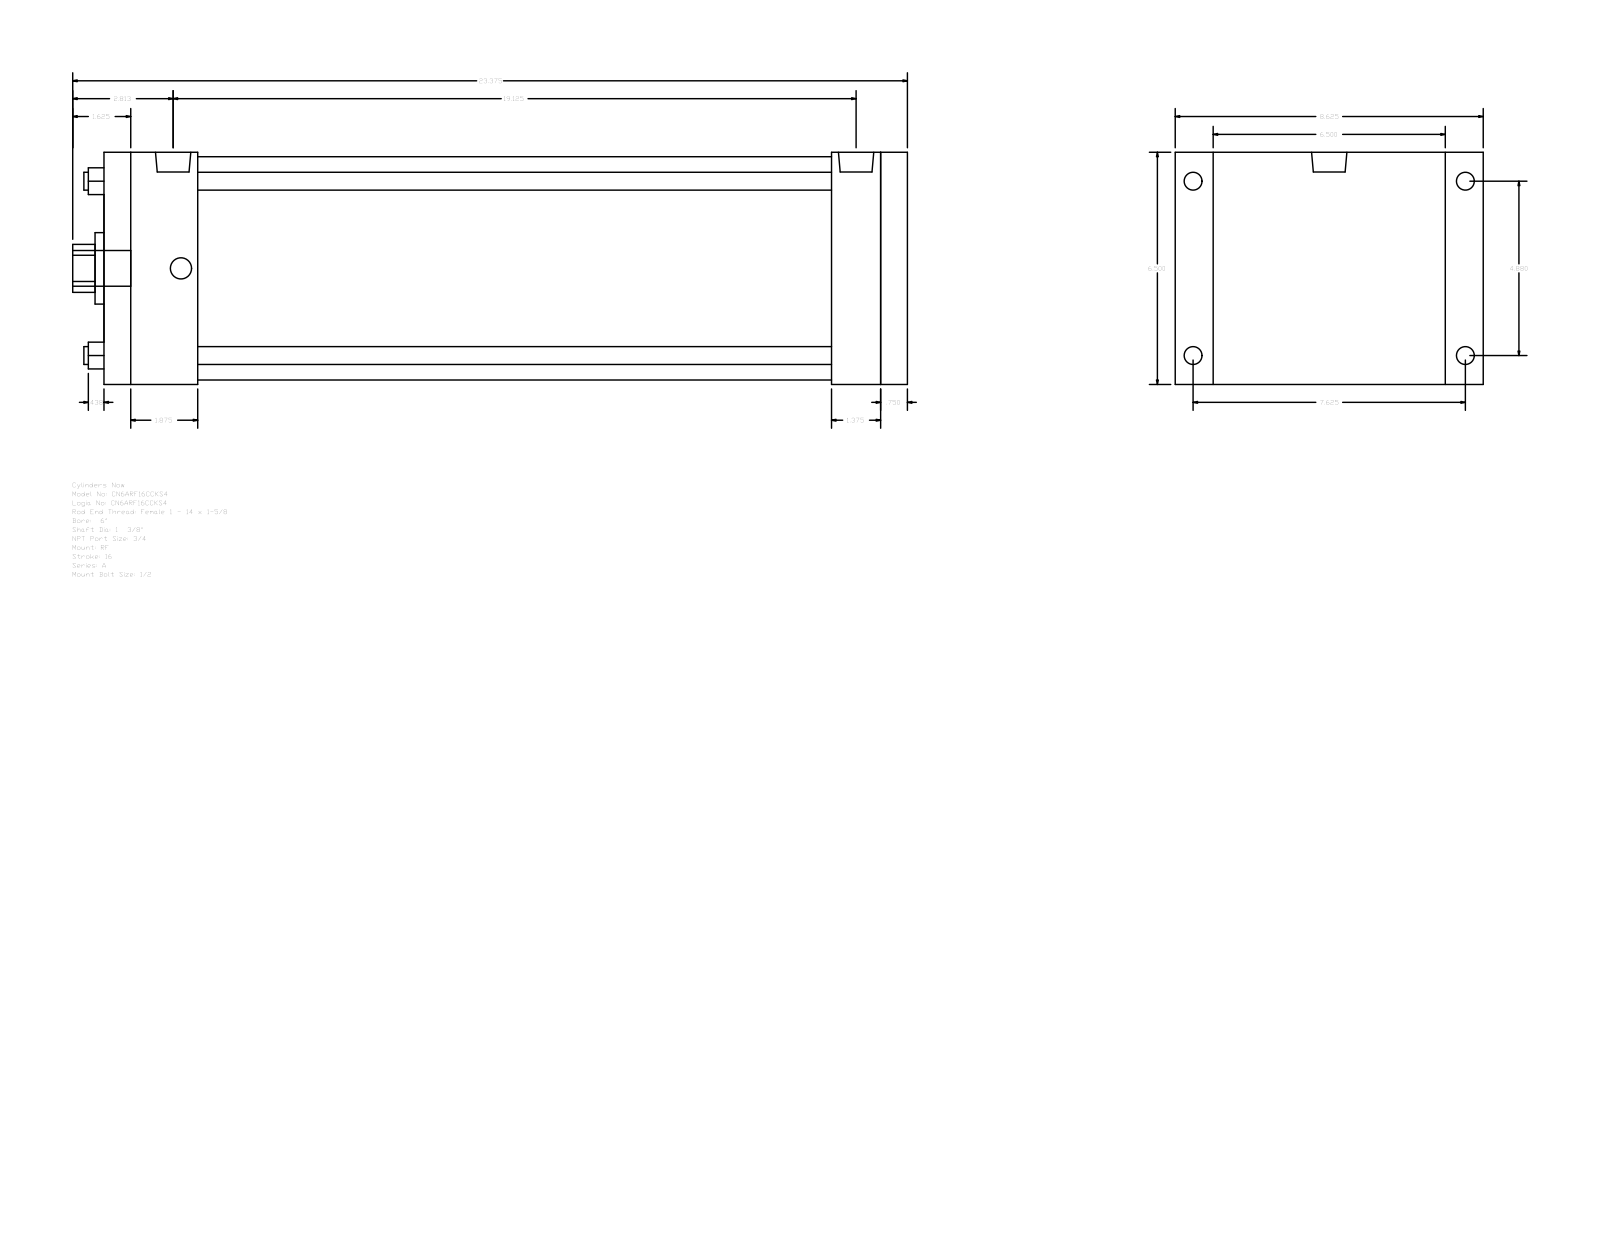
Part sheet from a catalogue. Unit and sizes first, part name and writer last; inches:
Units: inches
Overall size (bounding box): 23.375 × 8.625 × 6.5
Round holes (diameter × count): ⌀0.5 ×4, ⌀1.375 ×1, ⌀2 ×1, ⌀6.25 ×1
Round bosses / shafts (diameter × count): ⌀0.594 ×4, ⌀0.5 ×4, ⌀0.989 ×2, ⌀1 ×1
Partial cylindrical surfaces — rounded edges, fillets, slot ends (radius × count): R0.672 ×1
Main face-to-face distances: 6.5, 22.5, 21.75, 0.75, 2.625, 19.125, 19.875, 20.375, 17.75, 1.375
Hole centre spacings: 3.451, 4.88, 6.902
Bodies: 0 solids, 92 faces (64 planar, 28 cylindrical, 0 other)
Part name (STEP PRODUCT): A_RF__0600_1.375
STEP written by: GSSL Pune (CONFIG_CONTROL_DESIGN)
